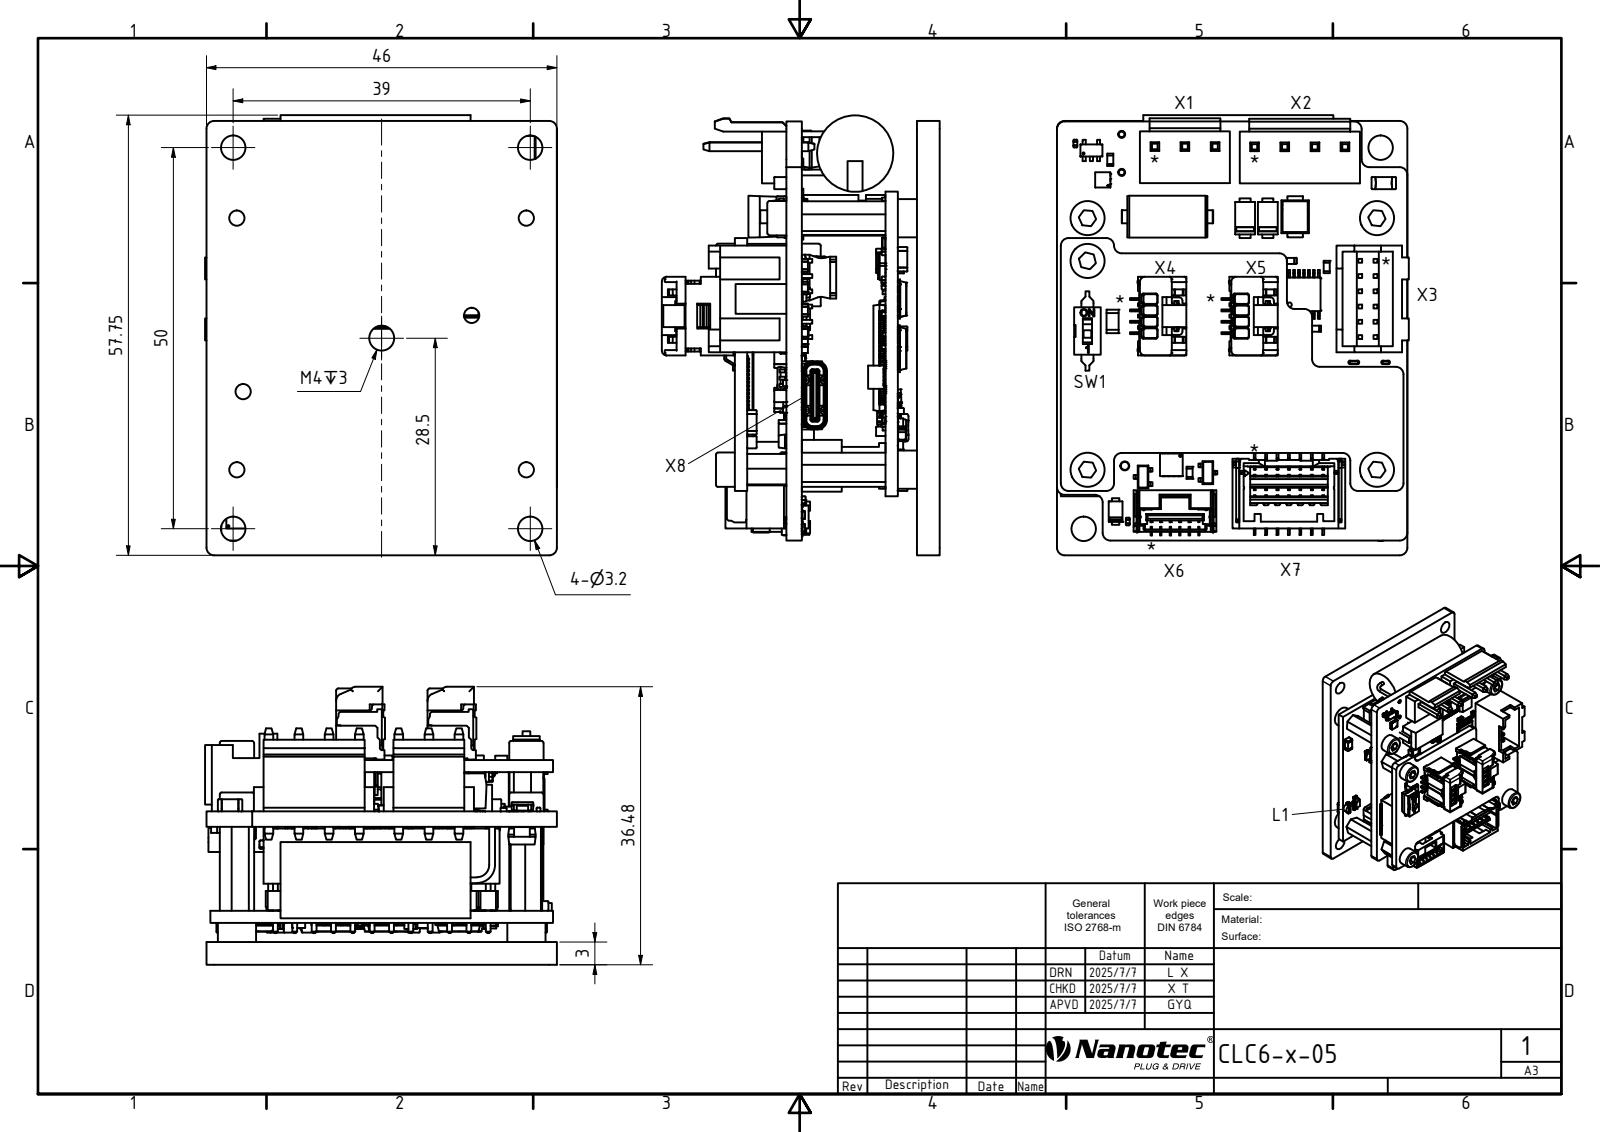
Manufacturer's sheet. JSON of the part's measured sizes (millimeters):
{"part_name": "CLC6-x-05", "step_written_by": "Autodesk Inventor 2024 (AUTOMOTIVE_DESIGN)", "units": "millimeters", "bodies": {"solids": 0, "faces": 29461, "planar": 21404, "cylindrical": 5333, "other": 2724}, "overall_size": [57.75, 46.2, 36.48], "round_holes": [[0.91, 24], [0.7, 12], [1.7, 7], [2.01, 7], [0.25, 4], [0.3, 4], [0.6, 4], [2.51, 4], [2.6, 4], [3.2, 4], [2.7, 3], [0.9, 2]], "round_bosses_or_shafts": [[0.4, 8], [4.5, 5], [2.5, 5], [5, 4], [1.14, 4], [1.03, 4], [1.02, 4], [0.76, 4]], "partial_cylinders_radius": [[0.1, 1132], [0.2, 148], [0.15, 62], [0.13, 50], [0.21, 50], [0.12, 48], [1, 35], [0.3, 26]], "face_to_face_distances": [2.02, 18.11, 17.13, 3, 20.13, 15.11, 2.5, 5.5, 14.63, 12.61], "hole_center_spacings": [2.54, 5.08, 5.68, 3.59, 7.62, 8.03, 10.16, 10.47]}
